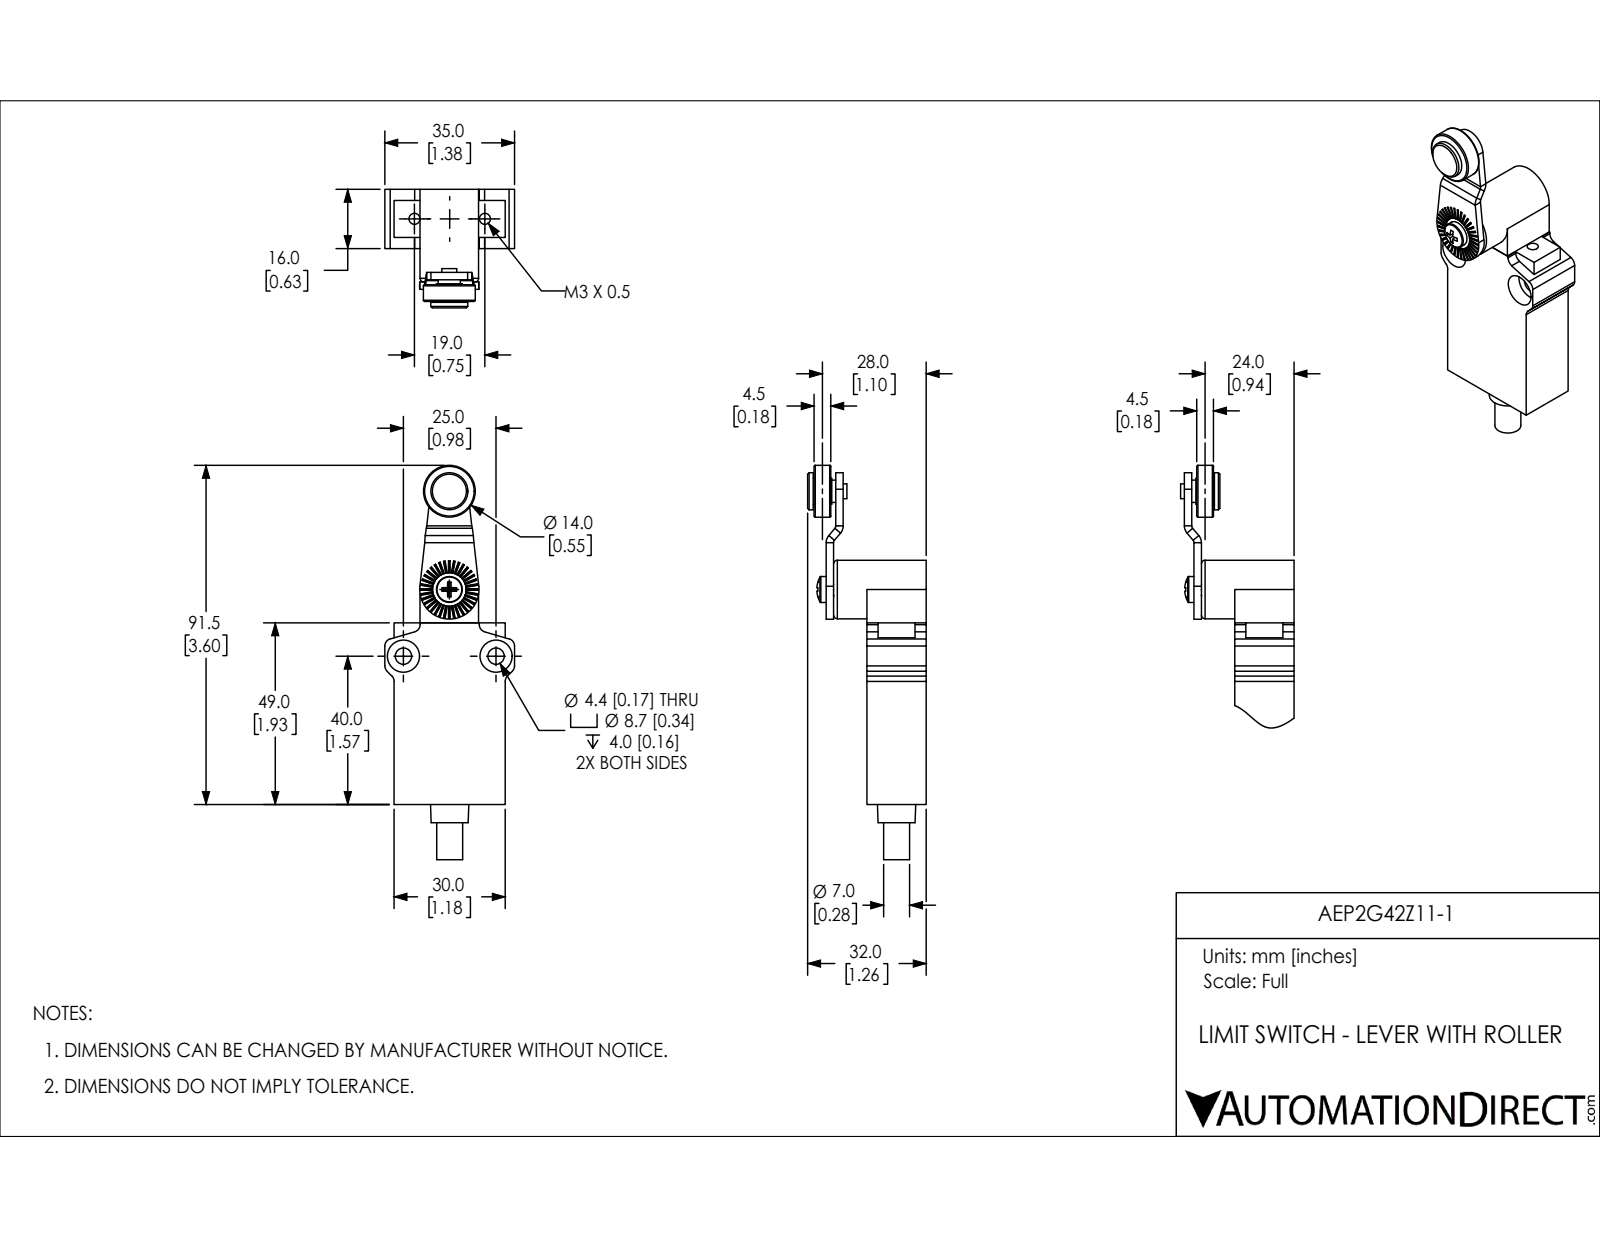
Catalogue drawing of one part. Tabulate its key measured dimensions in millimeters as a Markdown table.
| quantity | value |
| --- | --- |
| part name | AEP2G42Z11-1 |
| STEP written by | SolidWorks 2018 (AUTOMOTIVE_DESIGN) |
| units | millimeters |
| bodies | 6 solids, 586 faces (295 planar, 119 cylindrical, 172 other) |
| overall size | 106.4 × 35 × 32 |
| volume | 30 370 mm³ |
| surface area | 11 350 mm² |
| round holes (diameter × count) | 3 × 2, 4.4 × 2, 5 × 2, 8.7 × 2, 2.5 × 1, 4.1 × 1, 5.7 × 1 |
| round bosses / shafts (diameter × count) | 7 × 3, 15.8 × 1, 14 × 1, 10 × 1, 6 × 1, 4 × 1, 3.5 × 1 |
| partial cylindrical surfaces (radius × count) | 2 × 8, 1 × 2, 3 × 2, 6.5 × 1, 8 × 1 |
| main face-to-face distances | 16, 30, 9, 49, 2, 25, 2.6, 12, 23, 7 |
| hole center spacings | 19, 21.9, 22, 25, 26.5, 46.2, 46.3 |
